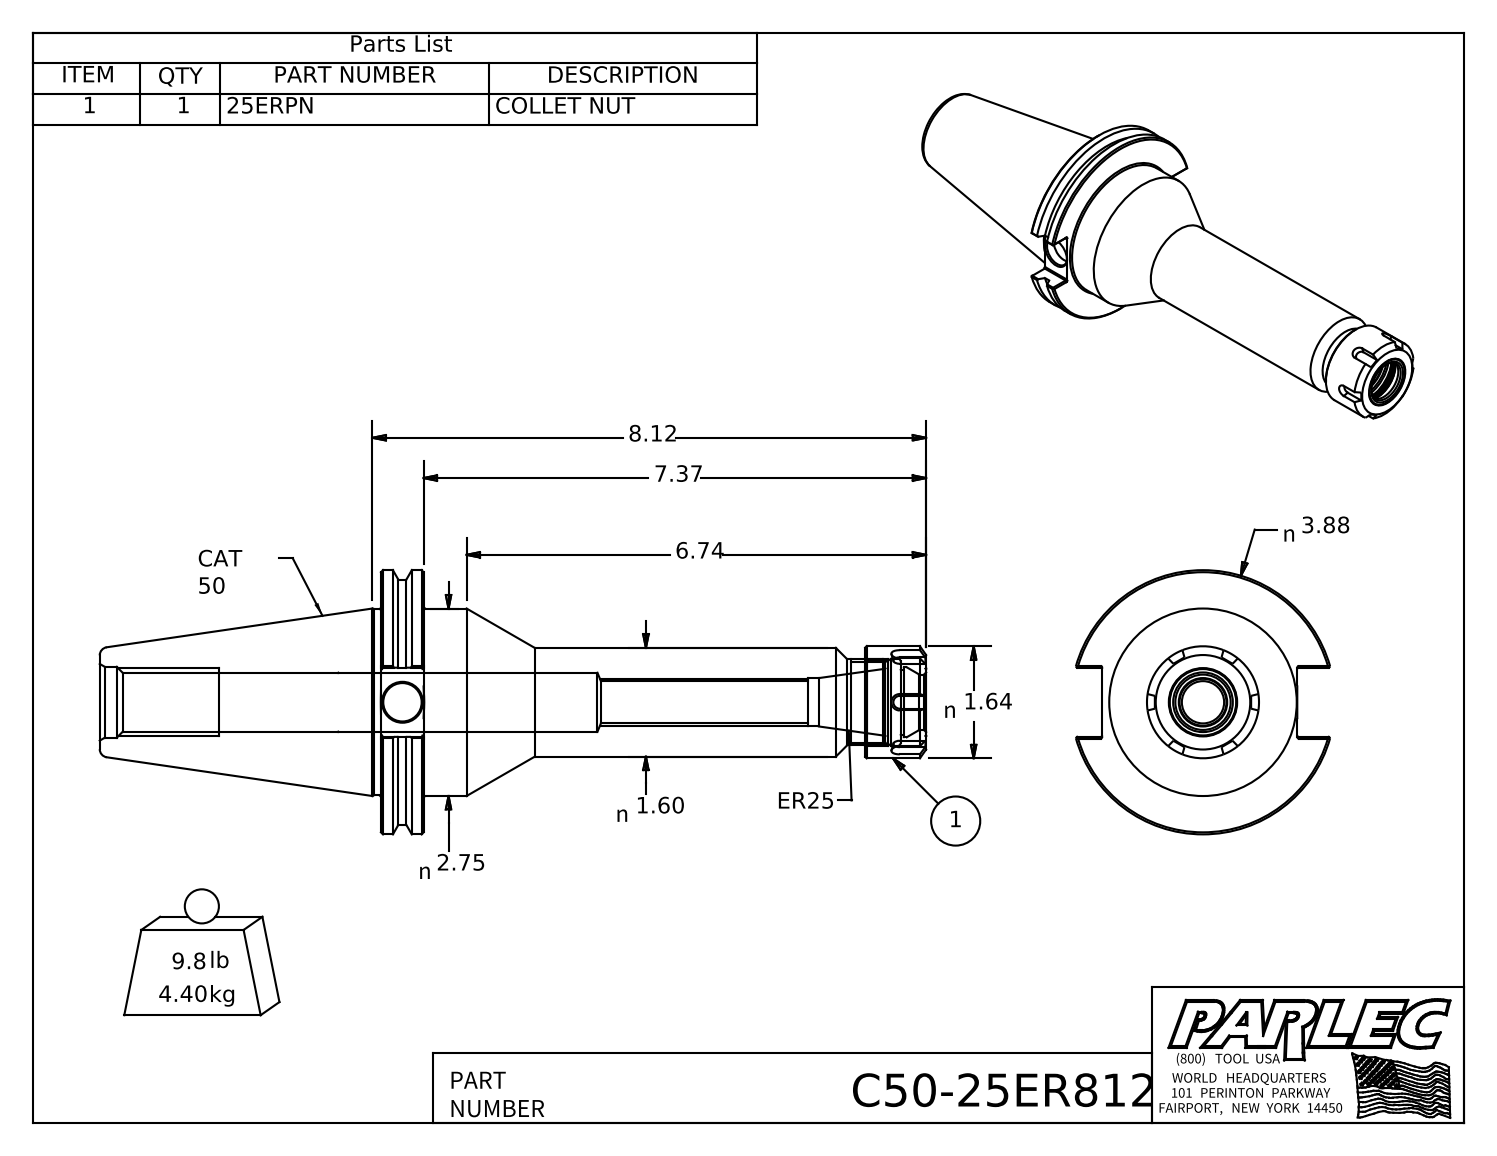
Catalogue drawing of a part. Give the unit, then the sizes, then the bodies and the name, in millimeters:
Units: millimetres
Overall size (bounding box): 307.8 × 98.4 × 94.7
Round holes (diameter × count): ⌀14.3 ×1, ⌀15.7 ×1, ⌀18 ×1, ⌀20.6 ×1, ⌀21.9 ×1, ⌀22 ×1, ⌀24.1 ×1, ⌀26.1 ×1, ⌀26.4 ×1, ⌀30.9 ×1, ⌀32.5 ×1
Round bosses / shafts (diameter × count): ⌀98.4 ×1, ⌀91.3 ×1, ⌀69.9 ×1, ⌀69.3 ×1, ⌀41.7 ×1, ⌀40.5 ×1, ⌀32 ×1
Partial cylindrical surfaces — rounded edges, fillets, slot ends (radius × count): R0.5 ×12
Main face-to-face distances: 15.9, 203.1, 187.2, 180.4, 164.5, 22.7, 104.8, 120.7, 285.2, 307.8
Volume: 566 700 mm³ · Surface area: 82 840 mm²
Bodies: 2 solids, 127 faces (50 planar, 34 cylindrical, 43 other)
Part name (STEP PRODUCT): C50-25ER812; C50-25ER8-1; 25ERPN
STEP written by: Autodesk Inventor 2012 (AUTOMOTIVE_DESIGN)
